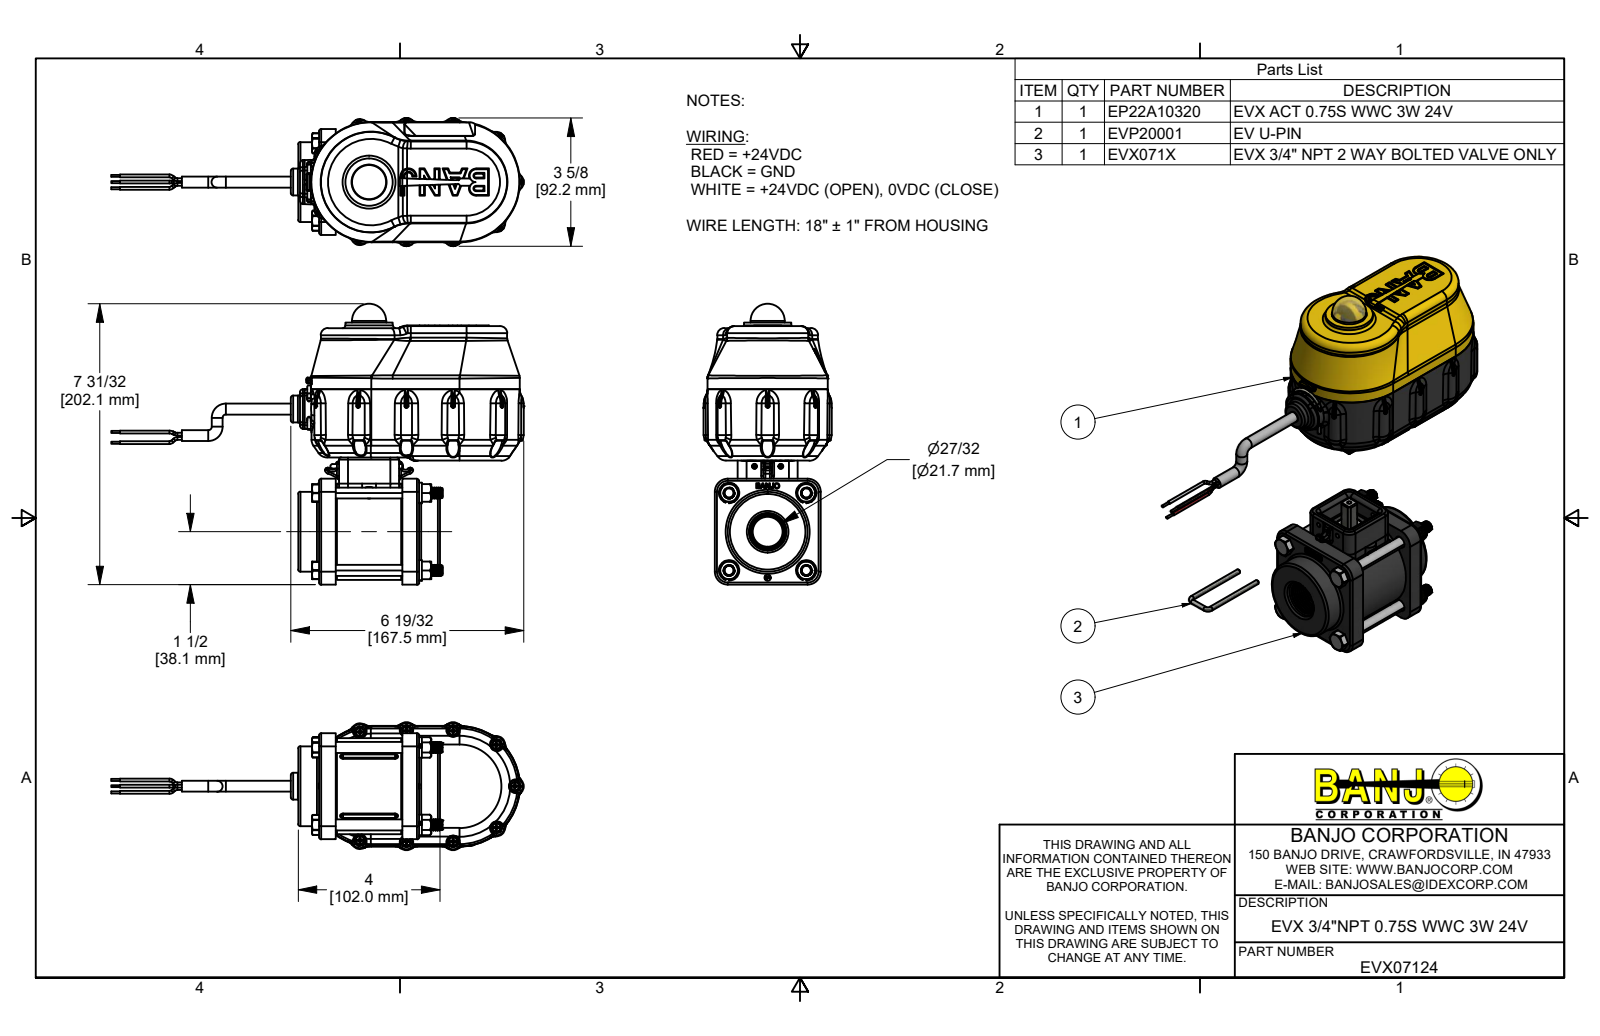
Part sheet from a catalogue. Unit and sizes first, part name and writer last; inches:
Units: inches
Overall size (bounding box): 30.214 × 7.957 × 3.63
Round holes (diameter × count): ⌀0.095 ×11, ⌀0.15 ×11, ⌀0.08 ×7, ⌀0.107 ×4, ⌀0.126 ×4, ⌀0.136 ×4, ⌀0.148 ×4, ⌀0.15 ×4, ⌀0.17 ×4, ⌀0.252 ×4, ⌀0.322 ×4, ⌀0.35 ×4
Round bosses / shafts (diameter × count): ⌀0.268 ×60, ⌀0.25 ×17, ⌀0.08 ×15, ⌀0.14 ×11, ⌀0.108 ×11, ⌀0.085 ×11, ⌀0.058 ×6, ⌀0.313 ×5
Partial cylindrical surfaces — rounded edges, fillets, slot ends (radius × count): R0.013 ×180, R0.04 ×145, R0.01 ×92, R0.02 ×71, R0.06 ×58, R0.005 ×53, R0.03 ×38, R0.08 ×28
Main face-to-face distances: 0.1, 2.565, 0.211, 0.06, 0.151, 2.95, 1.685, 1.836, 1.896, 2.465
Hole centre spacings: 2.192, 1.283, 1.55, 2.656, 1.046, 1.513, 1.662, 1.891
Volume: 51.66 in³ · Surface area: 901.8 in²
Bodies: 96 solids, 11633 faces (2948 planar, 3477 cylindrical, 5208 other)
Part name (STEP PRODUCT): EVX07124; EP22A10320; B61905PPHS; B632038PM (+8 more)
STEP written by: Autodesk Inventor 2019 (AUTOMOTIVE_DESIGN)
